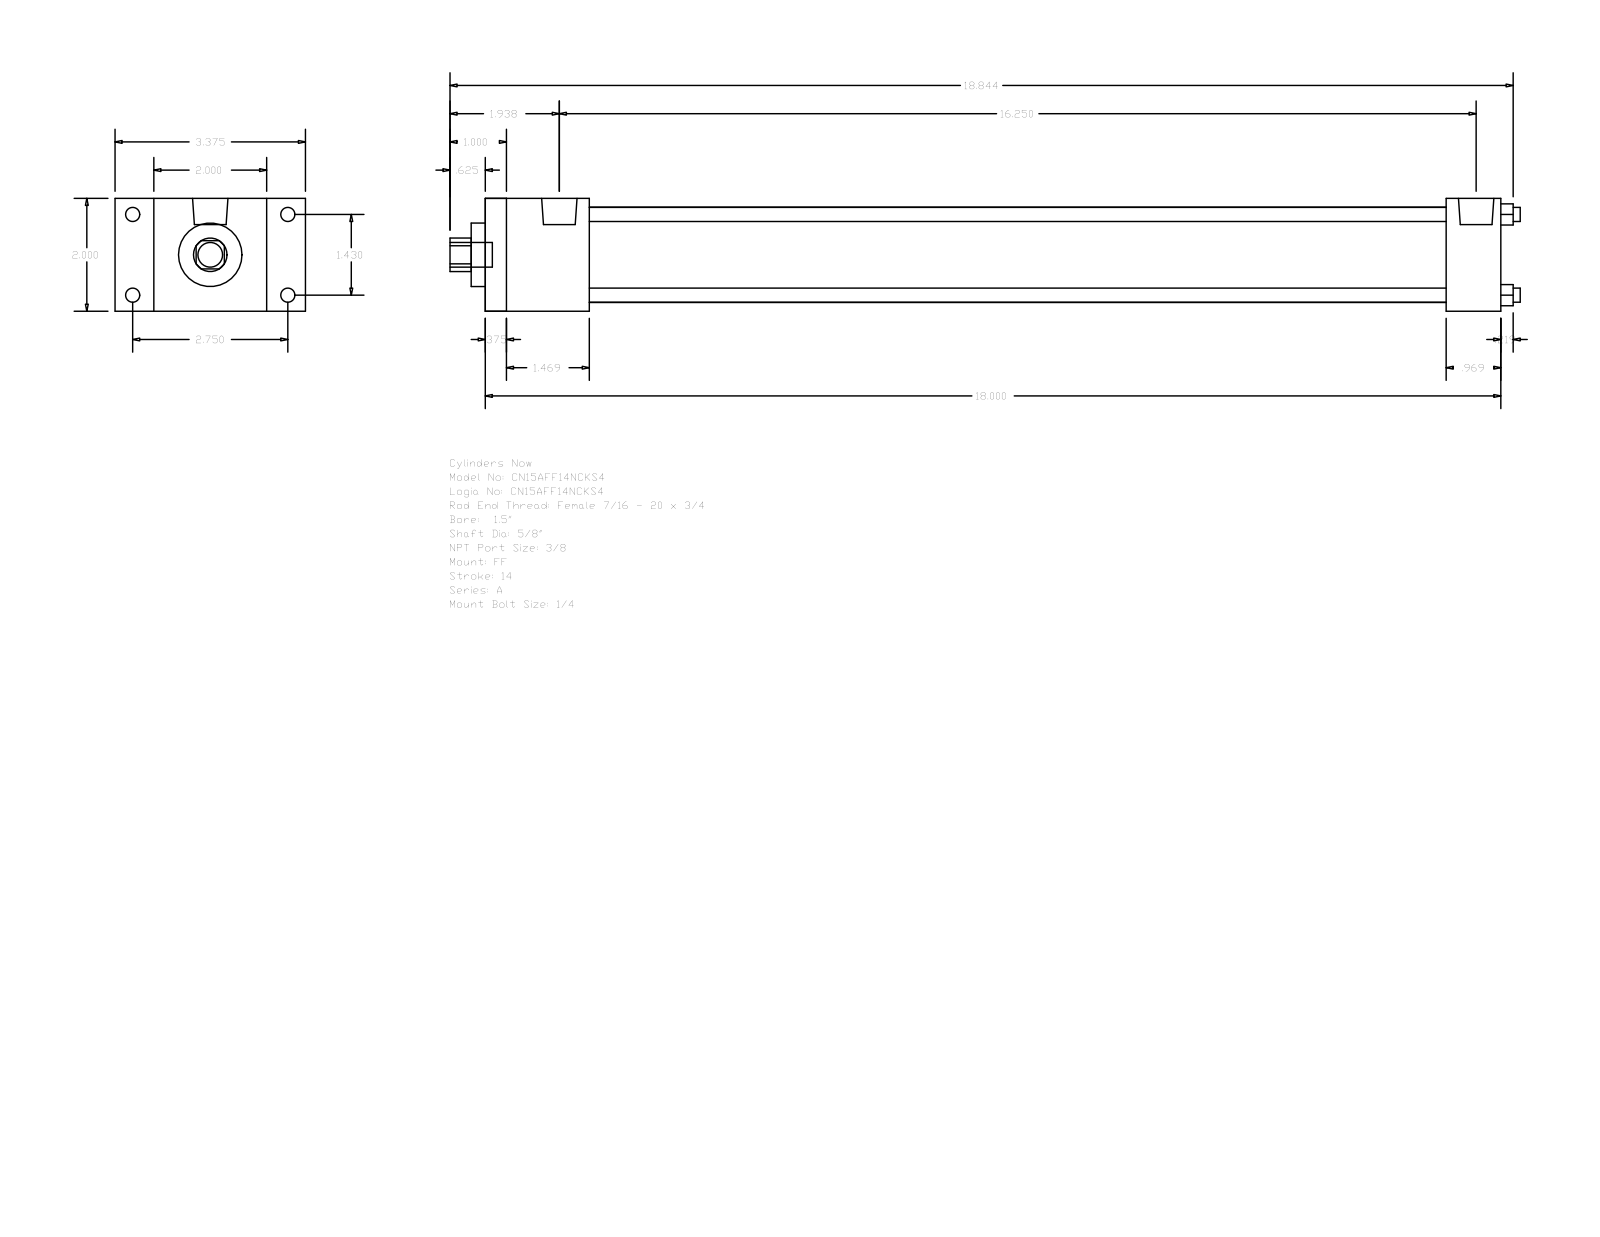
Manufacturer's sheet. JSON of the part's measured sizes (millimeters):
{"part_name": "A_FF__0150_0.625", "step_written_by": "GSSL Pune (CONFIG_CONTROL_DESIGN)", "units": "millimeters", "bodies": {"solids": 0, "faces": 92, "planar": 64, "cylindrical": 28, "other": 0}, "overall_size": [481.81, 85.72, 50.8], "round_holes": [[6.35, 4], [15.88, 1], [28.57, 1], [42.93, 1]], "round_bosses_or_shafts": [[6.35, 4], [5.56, 4], [15.93, 2], [11.11, 1]], "partial_cylinders_radius": [[7.54, 1]], "face_to_face_distances": [50.8, 457.19, 9.52, 447.67, 46.83, 432.59, 37.31, 423.07, 385.76, 410.36], "hole_center_spacings": [25.68, 36.32, 51.36]}
